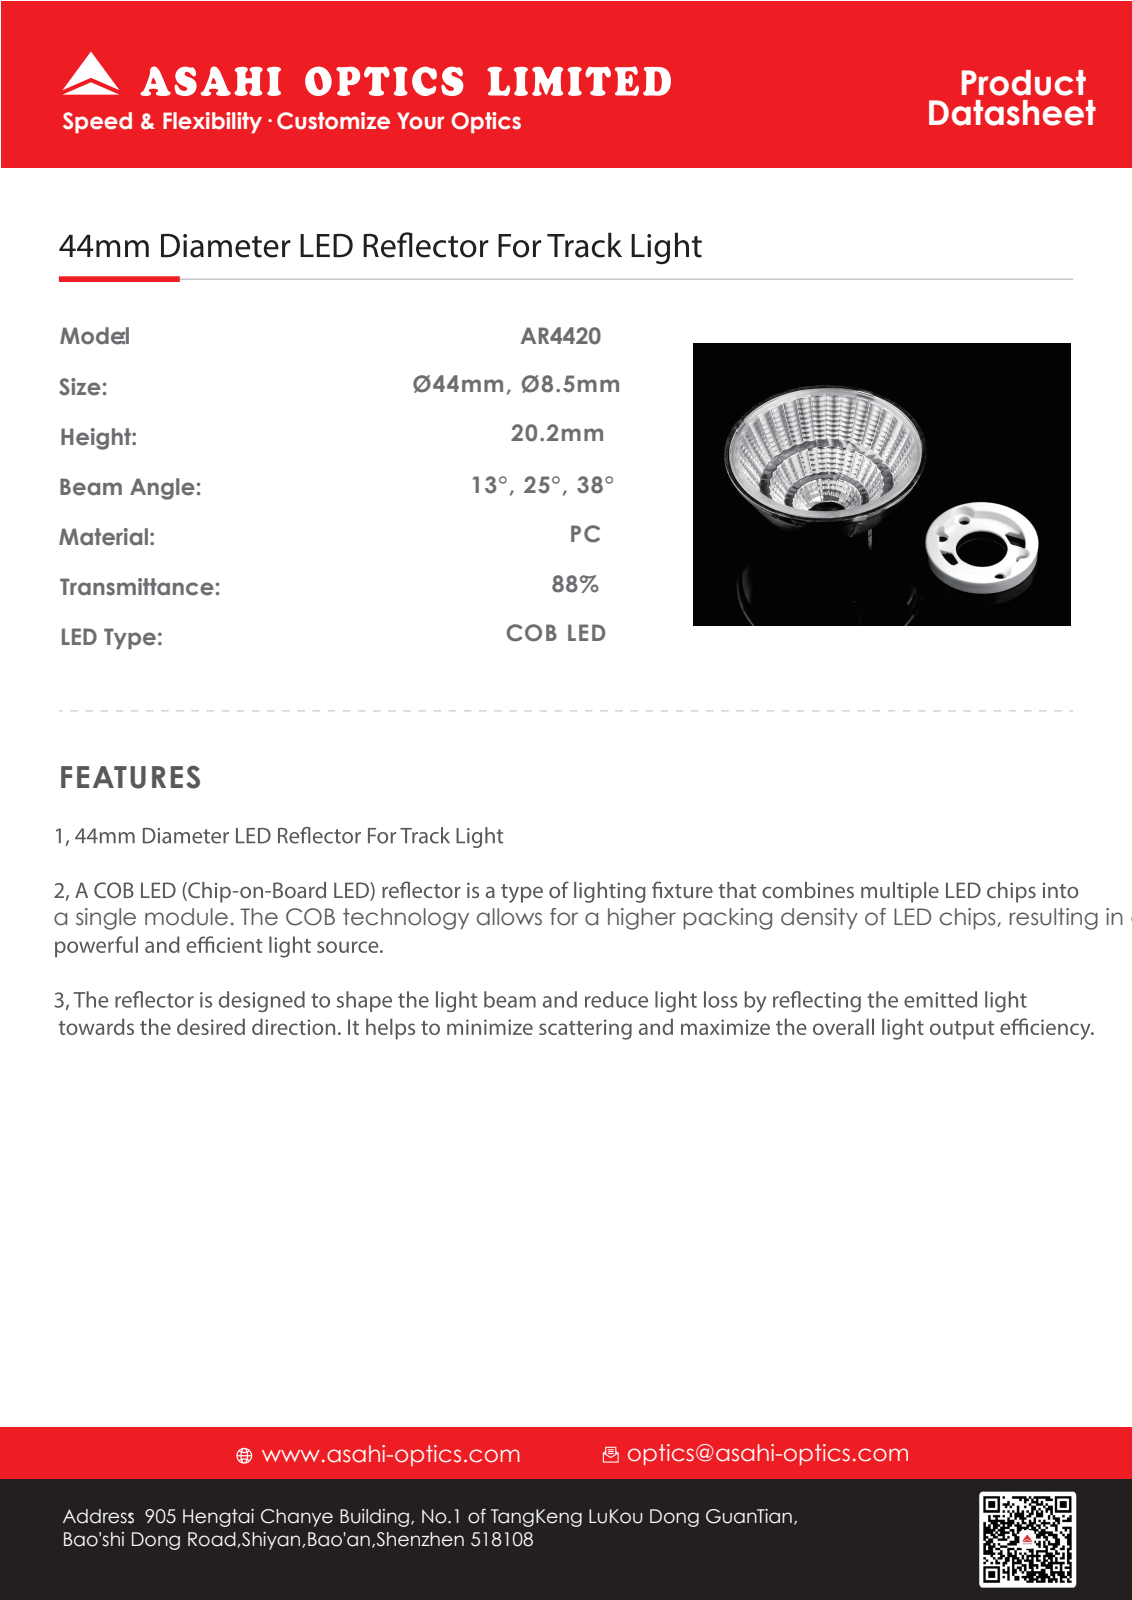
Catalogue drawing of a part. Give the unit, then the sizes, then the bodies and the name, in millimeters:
Units: millimetres
Overall size (bounding box): 44 × 44 × 21.65
Round holes (diameter × count): ⌀41.6 ×1
Round bosses / shafts (diameter × count): ⌀2.75 ×2, ⌀44 ×1
Partial cylindrical surfaces — rounded edges, fillets, slot ends (radius × count): R20.43 ×1
Main face-to-face distances: 1.55, 18.6, 20.15, 19.55, 0.95, 0.6, 1.5, 20.1, 21.05, 21.65
Volume: 2 611 mm³ · Surface area: 5 275 mm²
Bodies: 1 solid, 830 faces (25 planar, 14 cylindrical, 791 other)
Part name (STEP PRODUCT): SL-04415B-20140113
STEP written by: SolidWorks 2014 (CONFIG_CONTROL_DESIGN)
